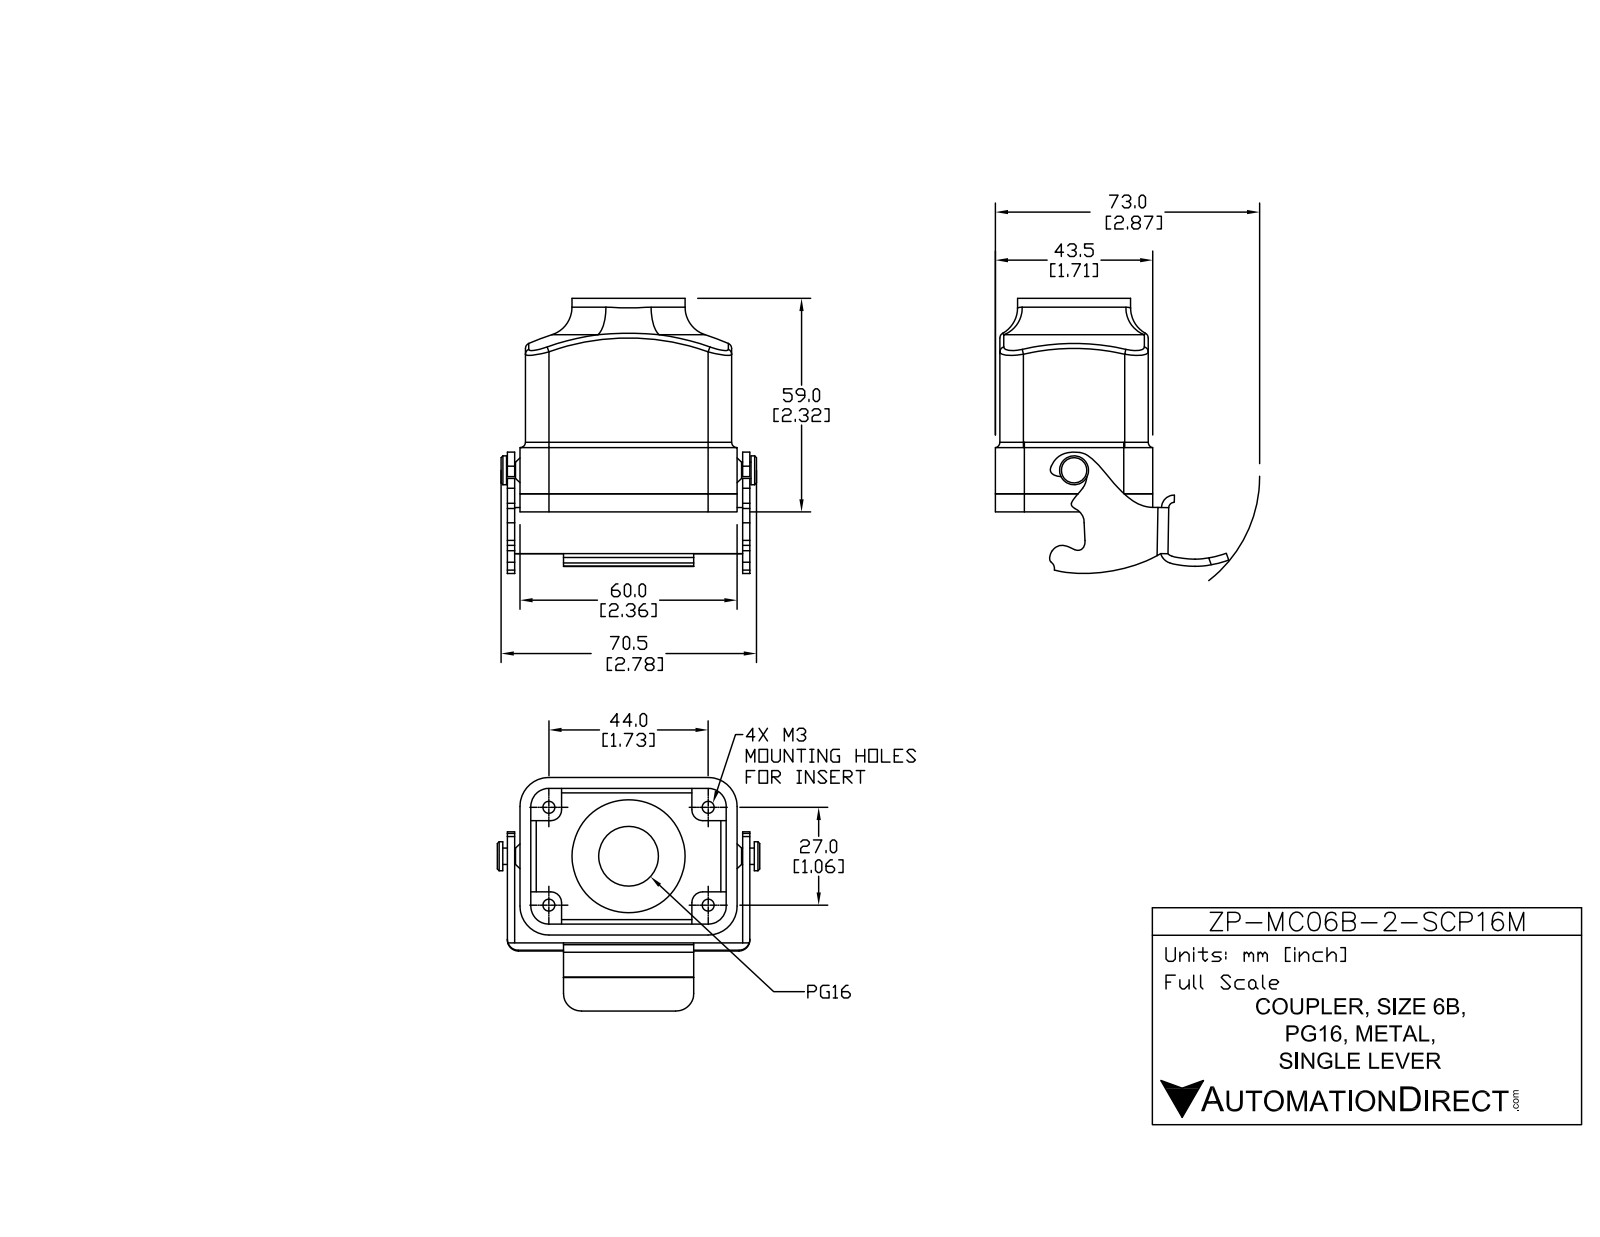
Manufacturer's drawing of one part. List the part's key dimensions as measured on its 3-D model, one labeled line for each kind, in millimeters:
Part name (STEP PRODUCT): ZP-MC06B-2-SCP16M
STEP written by: SolidWorks 2011 (AUTOMOTIVE_DESIGN)
Units: millimetres
Bodies: 5 solids, 265 faces (91 planar, 116 cylindrical, 58 other)
Overall size (bounding box): 72.5 × 72.35 × 59
Volume: 45 939 mm³ · Surface area: 32 210 mm²
Round holes (diameter × count): ⌀3.5 ×4, ⌀16.5 ×1, ⌀21 ×1
Round bosses / shafts (diameter × count): ⌀31.25 ×1, ⌀8 ×1, ⌀4.52 ×1
Partial cylindrical surfaces — rounded edges, fillets, slot ends (radius × count): R0.5 ×10, R0.12 ×6, R3 ×5, R5 ×5, R1 ×4, R1.5 ×4, R4.5 ×4, R6.5 ×4
Main face-to-face distances: 3, 1.25, 39.25, 1.5, 4.25, 38, 1.15, 55.5, 54, 42.25
Hole centre spacings: 27.72, 30.5, 46.3, 55.44
